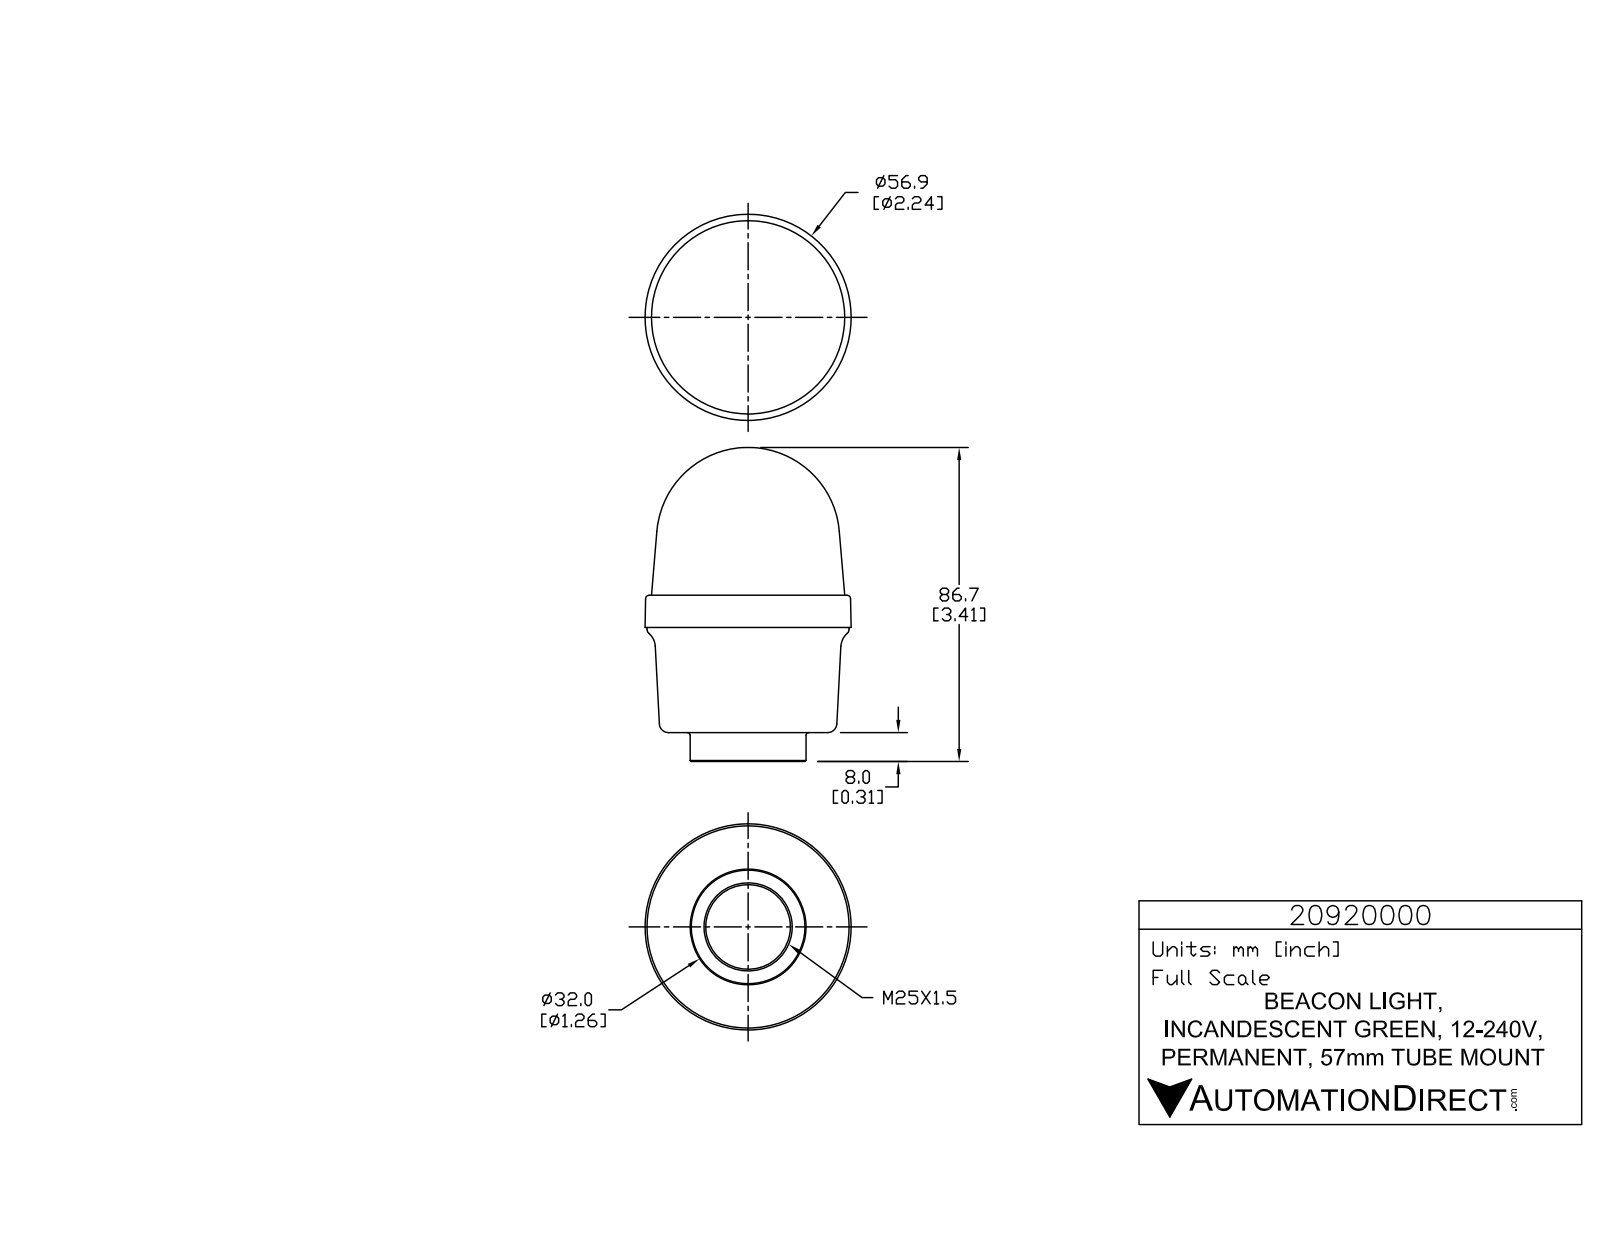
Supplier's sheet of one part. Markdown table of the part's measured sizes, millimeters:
| quantity | value |
| --- | --- |
| part name | 20920000 |
| STEP written by | SolidWorks 2015 (AUTOMOTIVE_DESIGN) |
| units | millimeters |
| bodies | 1 solid, 787 faces (524 planar, 168 cylindrical, 95 other) |
| overall size | 86.7 × 56.9 × 56.9 |
| volume | 150 600 mm³ |
| surface area | 16 310 mm² |
| round holes (diameter × count) | 1 × 3, 23.4 × 1 |
| round bosses / shafts (diameter × count) | 5.7 × 3, 1.4 × 3, 55.8 × 1, 32 × 1 |
| partial cylindrical surfaces (radius × count) | 0.2 × 6, 0.2 × 6, 0.2 × 6, 3.3 × 6, 0.1 × 3, 0.1 × 3, 0.2 × 3, 0.2 × 3 |
| main face-to-face distances | 8, 37.9, 45.9, 8.9, 29, 37, 17.7, 8.8, 46.7, 54.7 |
